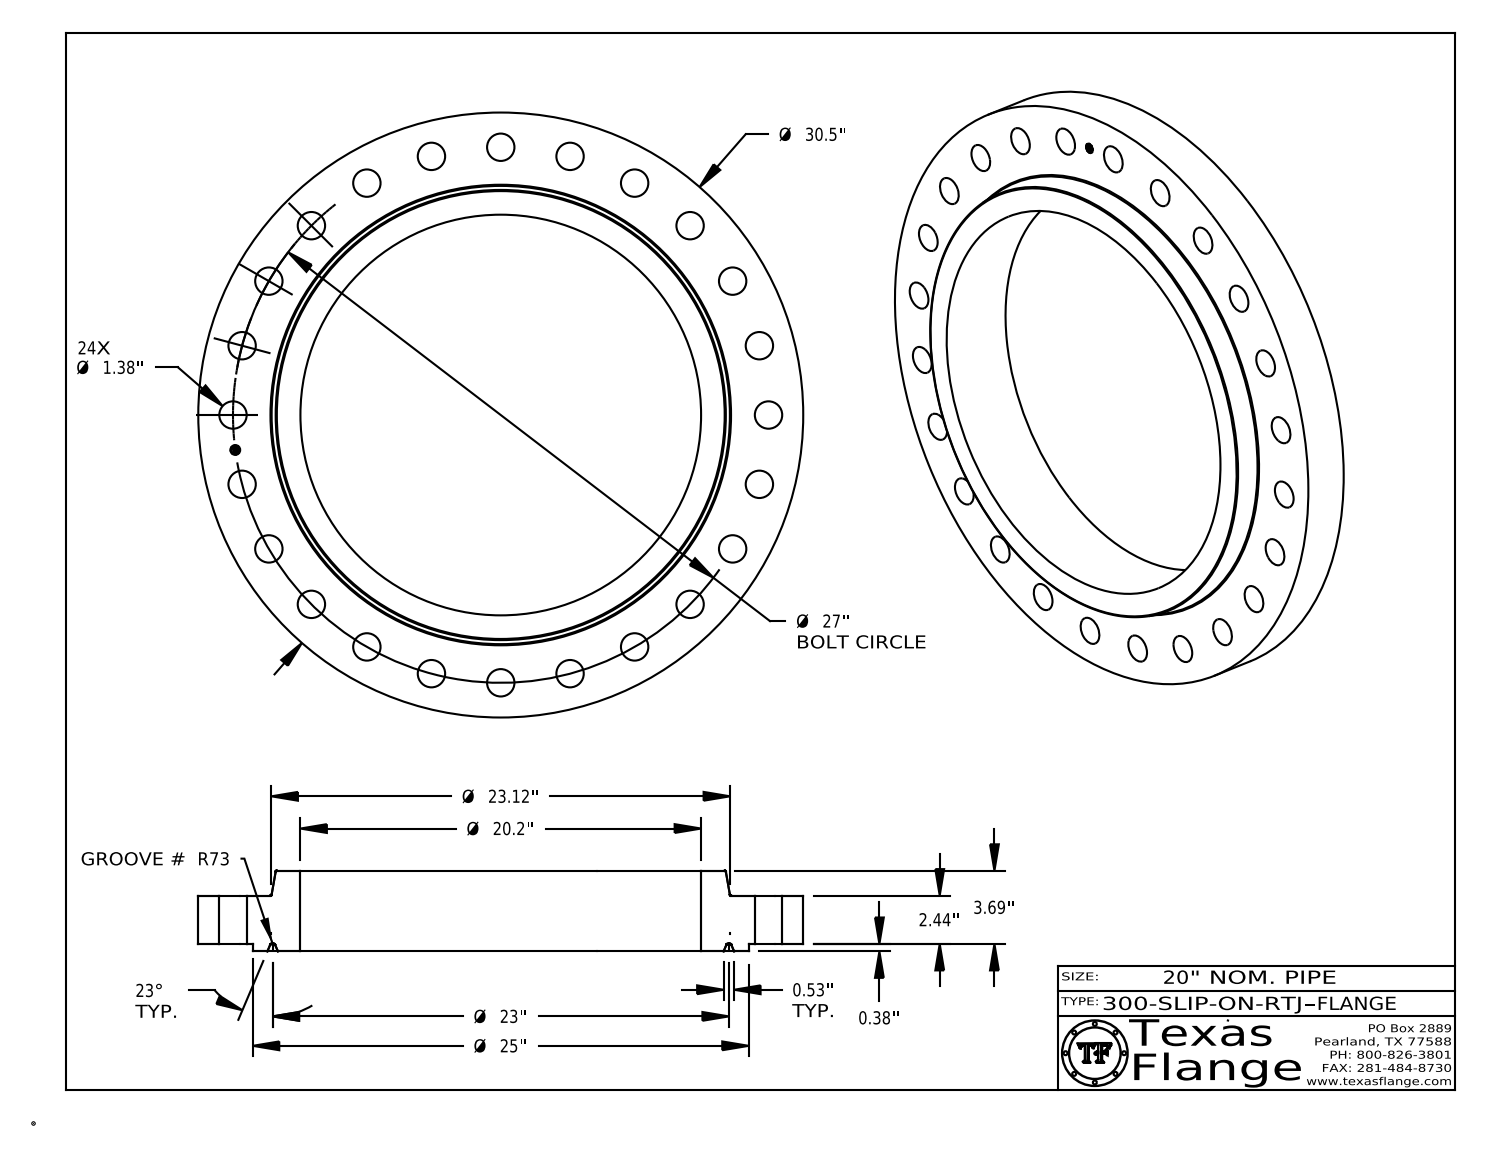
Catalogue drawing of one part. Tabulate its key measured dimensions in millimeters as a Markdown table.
| quantity | value |
| --- | --- |
| part name | 300-SLIP-ON-RTJ |
| STEP written by | CATIA V5 STEP AP214 (AUTOMOTIVE_DESIGN) |
| units | millimeters |
| bodies | 1 solid, 459 faces (371 planar, 74 cylindrical, 14 other) |
| overall size | 774.7 × 774.7 × 103.3 |
| volume | 17 710 000 mm³ |
| surface area | 1 052 000 mm² |
| round holes (diameter × count) | 35.1 × 24, 12.6 × 1, 513.1 × 1 |
| round bosses / shafts (diameter × count) | 0.8 × 8, 774.7 × 1, 635 × 1, 9.9 × 1 |
| main face-to-face distances | 62, 9.5, 71.5, 103.3, 93.7, 31.8, 71.1, 61.6, 0.4, 32.1 |
| hole center spacings | 342.9, 89.5, 177.5, 262.5, 417.5, 633.6, 679.9, 544.1 |
